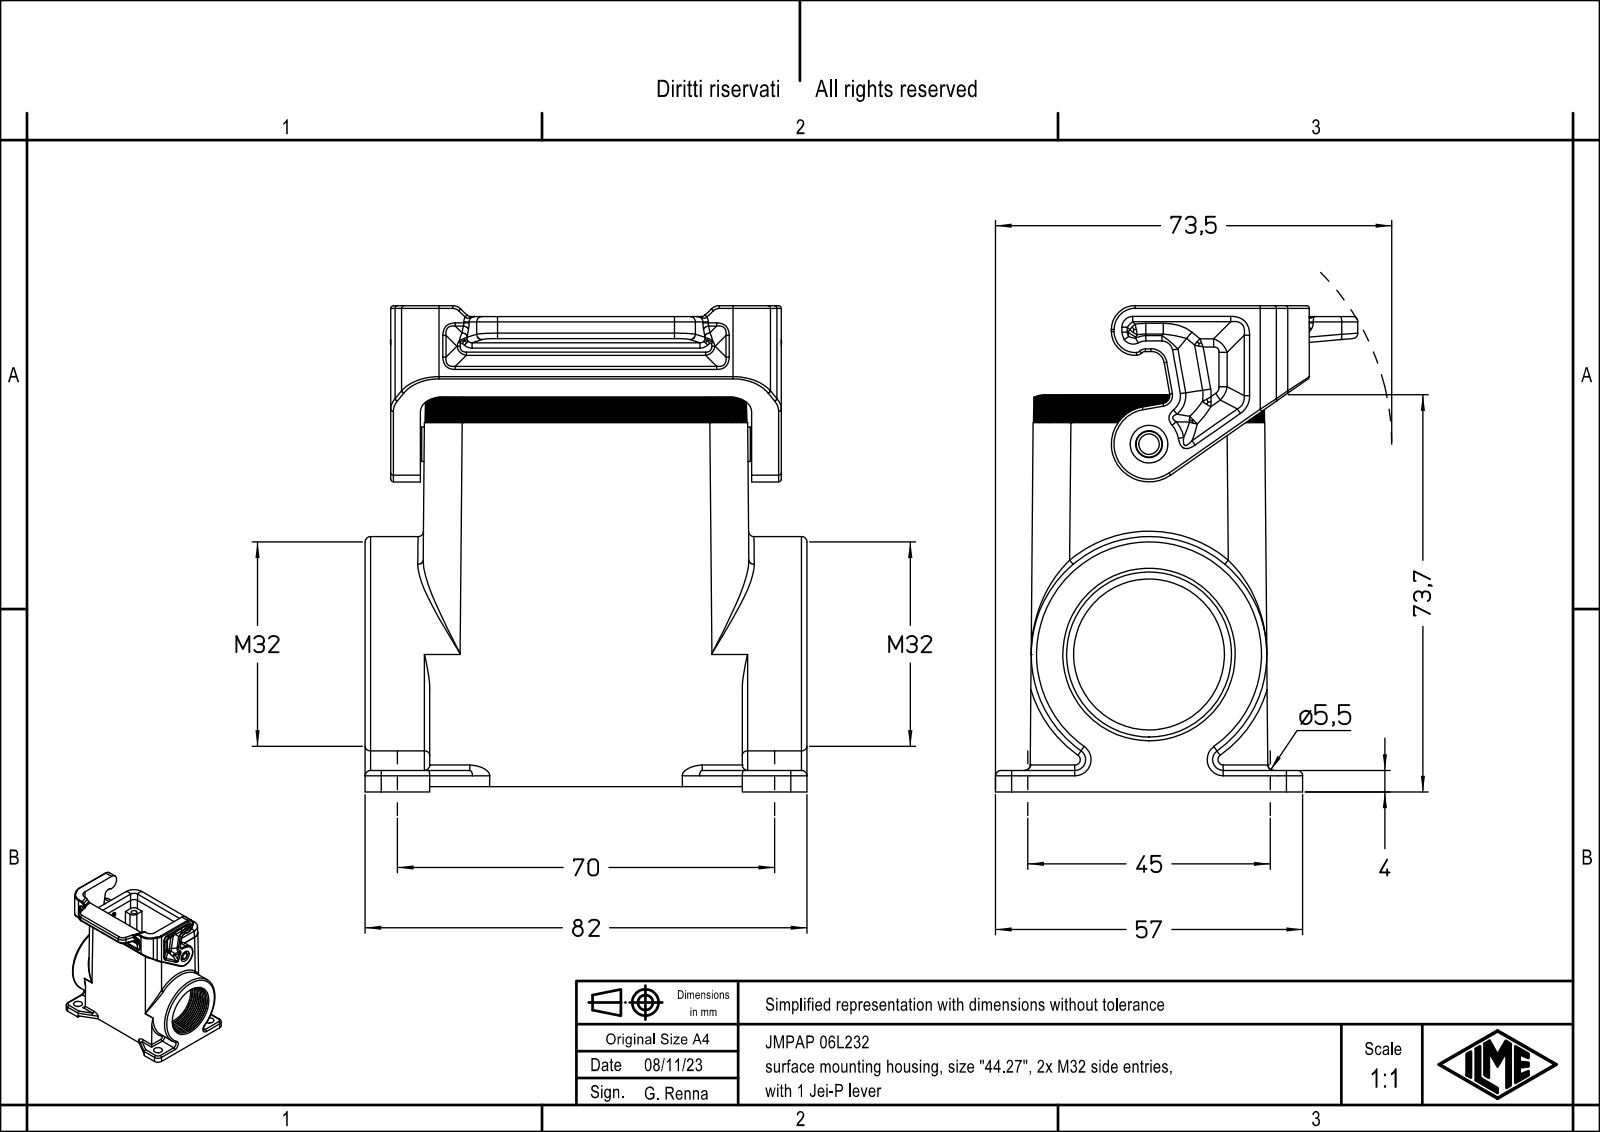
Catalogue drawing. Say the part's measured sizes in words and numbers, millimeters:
The part is named "JMPAP 06L232". Its 3-D file was written by "Creo Elements/Direct Modeling 20.1B 02-Apr-2019 (C) Parametric Technology GmbH (AUTOMOTIVE_DESIGN)". It is 1 solid with 514 faces: 120 planar, 176 cylindrical and 218 other. Overall it measures 90.2 by 82 by 67.25 millimeters. Its volume is 108 628 cubic millimeters and its surface area 44 663 square millimeters. Round holes: 4 of diameter 3.5, 1 of diameter 28, 1 of diameter 30.6. Round bosses or shafts: 1 of diameter 43.75, 1 of diameter 6.4, 1 of diameter 4.8. Partial cylindrical surfaces (rounded edges, fillets, slot ends): 31 of radius 1, 28 of radius 3, 18 of radius 0.5, 18 of radius 2, 9 of radius 7, 8 of radius 4, 6 of radius 6, 2 of radius 1.5. The main face-to-face distances are 3, 10.25, 71.75, 1, 4, 7, 82, 61.5, 2, 88.2. The hole center spacings are 27, 44, 51.62.
